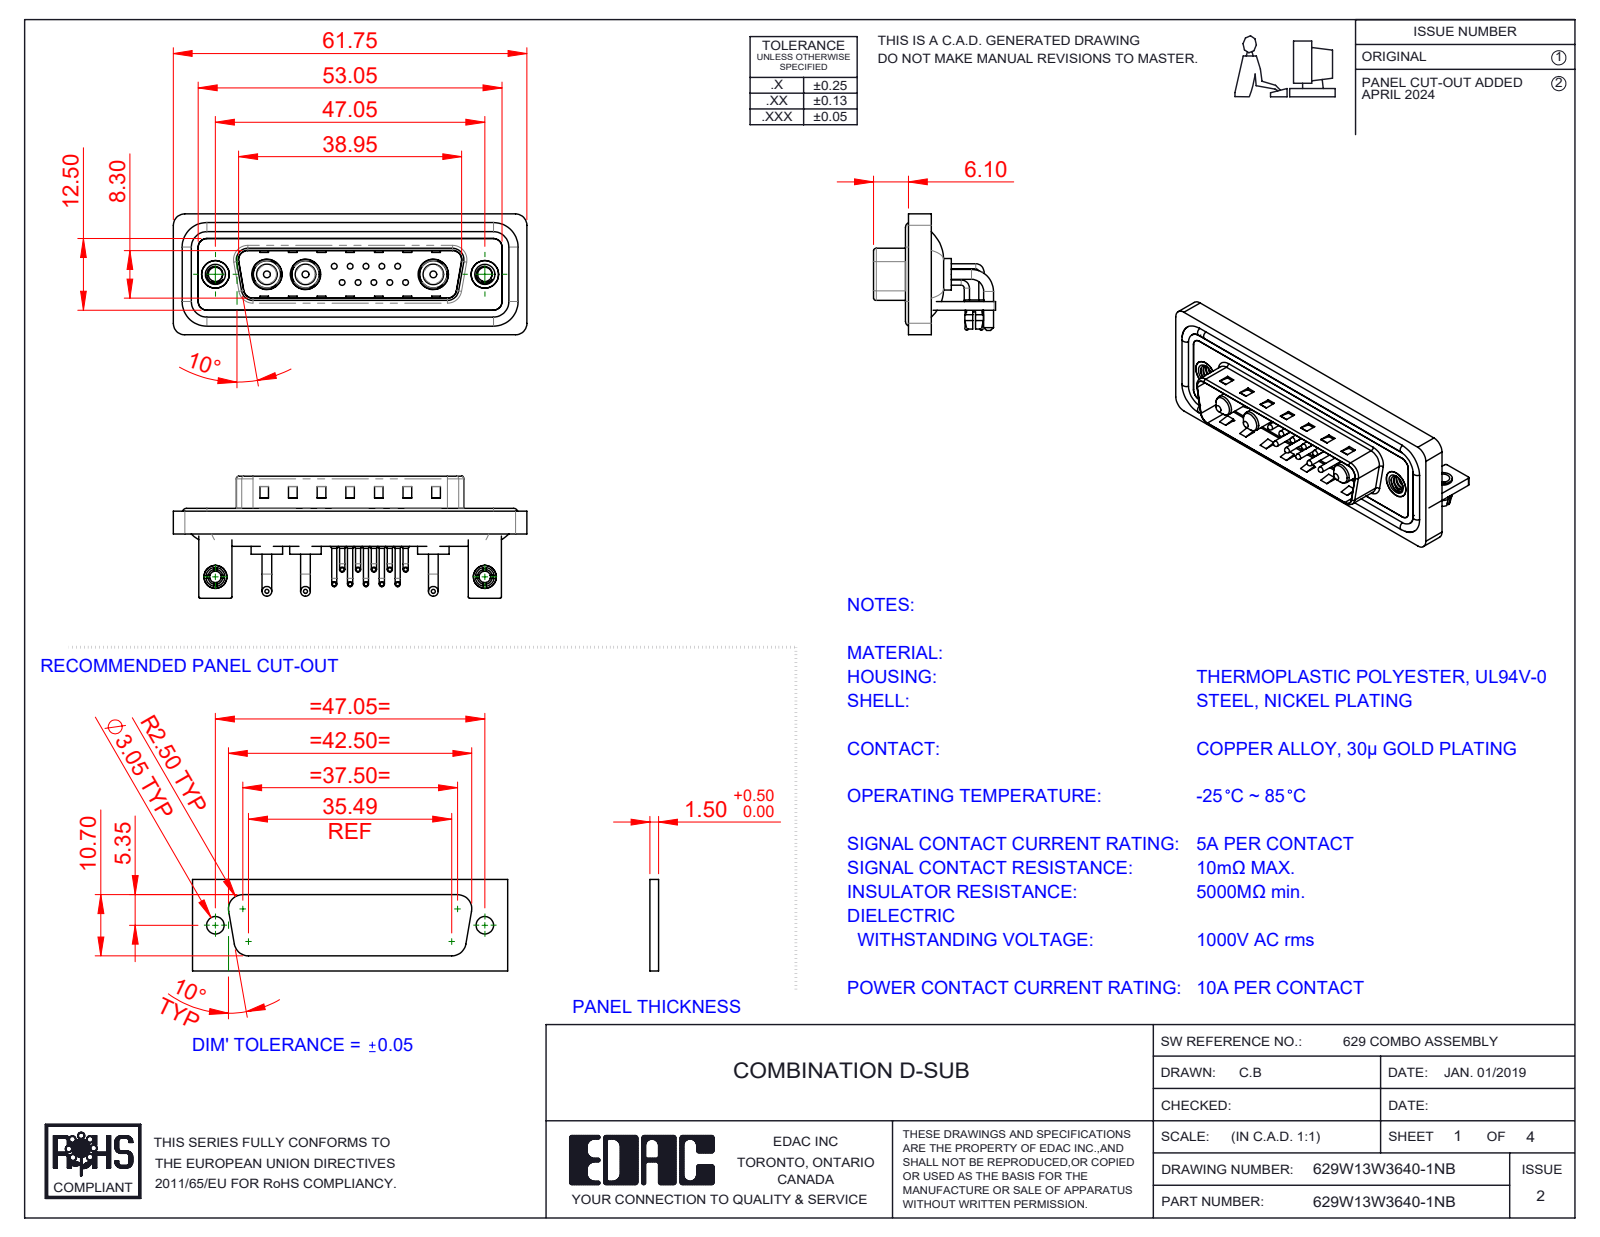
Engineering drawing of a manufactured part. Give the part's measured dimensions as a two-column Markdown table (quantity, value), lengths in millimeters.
| quantity | value |
| --- | --- |
| part name | 629Combo Contact Row 1; 629Combo Threaded Rivet_B; 629Combo Contact Row 2; 629Combo Shell Front_25 Contacts (+7 more) |
| STEP written by | SolidWorks 2023 (CONFIG_CONTROL_DESIGN) |
| units | millimeters |
| bodies | 27 solids, 1842 faces (947 planar, 661 cylindrical, 234 other) |
| overall size | 61.75 × 21.3 × 21.1 |
| volume | 7 744 mm³ |
| surface area | 13 142 mm² |
| round holes (diameter × count) | 2 × 12, 0.75 × 10, 1.6 × 10, 2.5 × 4, 4.85 × 3, 5.3 × 3, 3.2 × 2, 4 × 2, 4.8 × 2, 5 × 2 |
| round bosses / shafts (diameter × count) | 0.9 × 20, 1.5 × 10, 1 × 10, 0.65 × 10, 1.7 × 6, 1.6 × 4, 5.5 × 3, 5.2 × 3 |
| partial cylindrical surfaces (radius × count) | 2 × 19, 1.5 × 18, 0.25 × 16, 1.01 × 10, 0.5 × 9, 1.6 × 8, 0.6 × 4, 0.65 × 4 |
| main face-to-face distances | 0.4, 1.5, 0.8, 2.9, 2.1, 1.1, 4.1, 1.6, 3.7, 4.5 |
| hole center spacings | 3.16, 2.77, 5.04, 5.54, 7.49, 5.03, 8.31, 10.11 |
